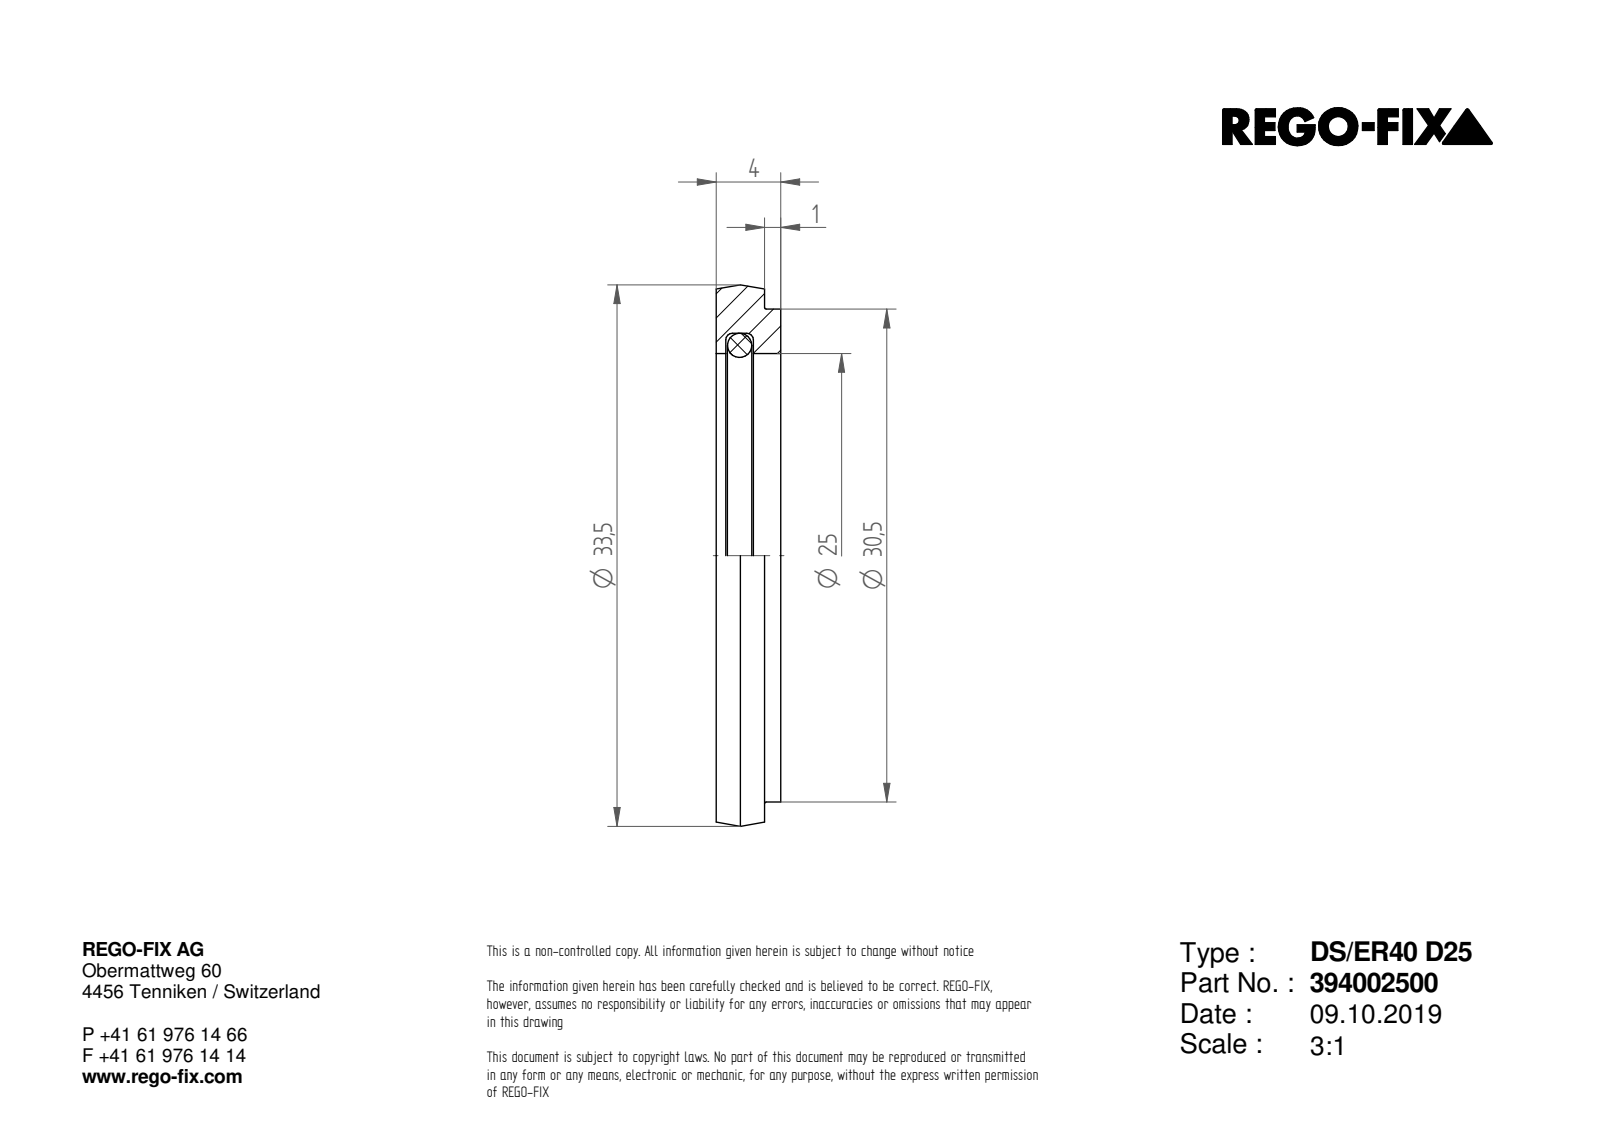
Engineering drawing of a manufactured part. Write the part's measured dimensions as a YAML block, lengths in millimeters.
part_name: "NOCUT"
step_written_by: "SIEMENS PLM Software Solid Edge ST10 (AUTOMOTIVE_DESIGN)"
units: millimeters
bodies: {solids: 1, faces: 7, planar: 3, cylindrical: 3, other: 1}
overall_size: [33.5, 33.5, 4]
volume: 1412
surface_area: 1503
round_holes:
  - {diameter: 25, count: 1}
round_bosses_or_shafts:
  - {diameter: 33.5, count: 1}
  - {diameter: 30.5, count: 1}
face_to_face_distances: [4, 1, 3]
